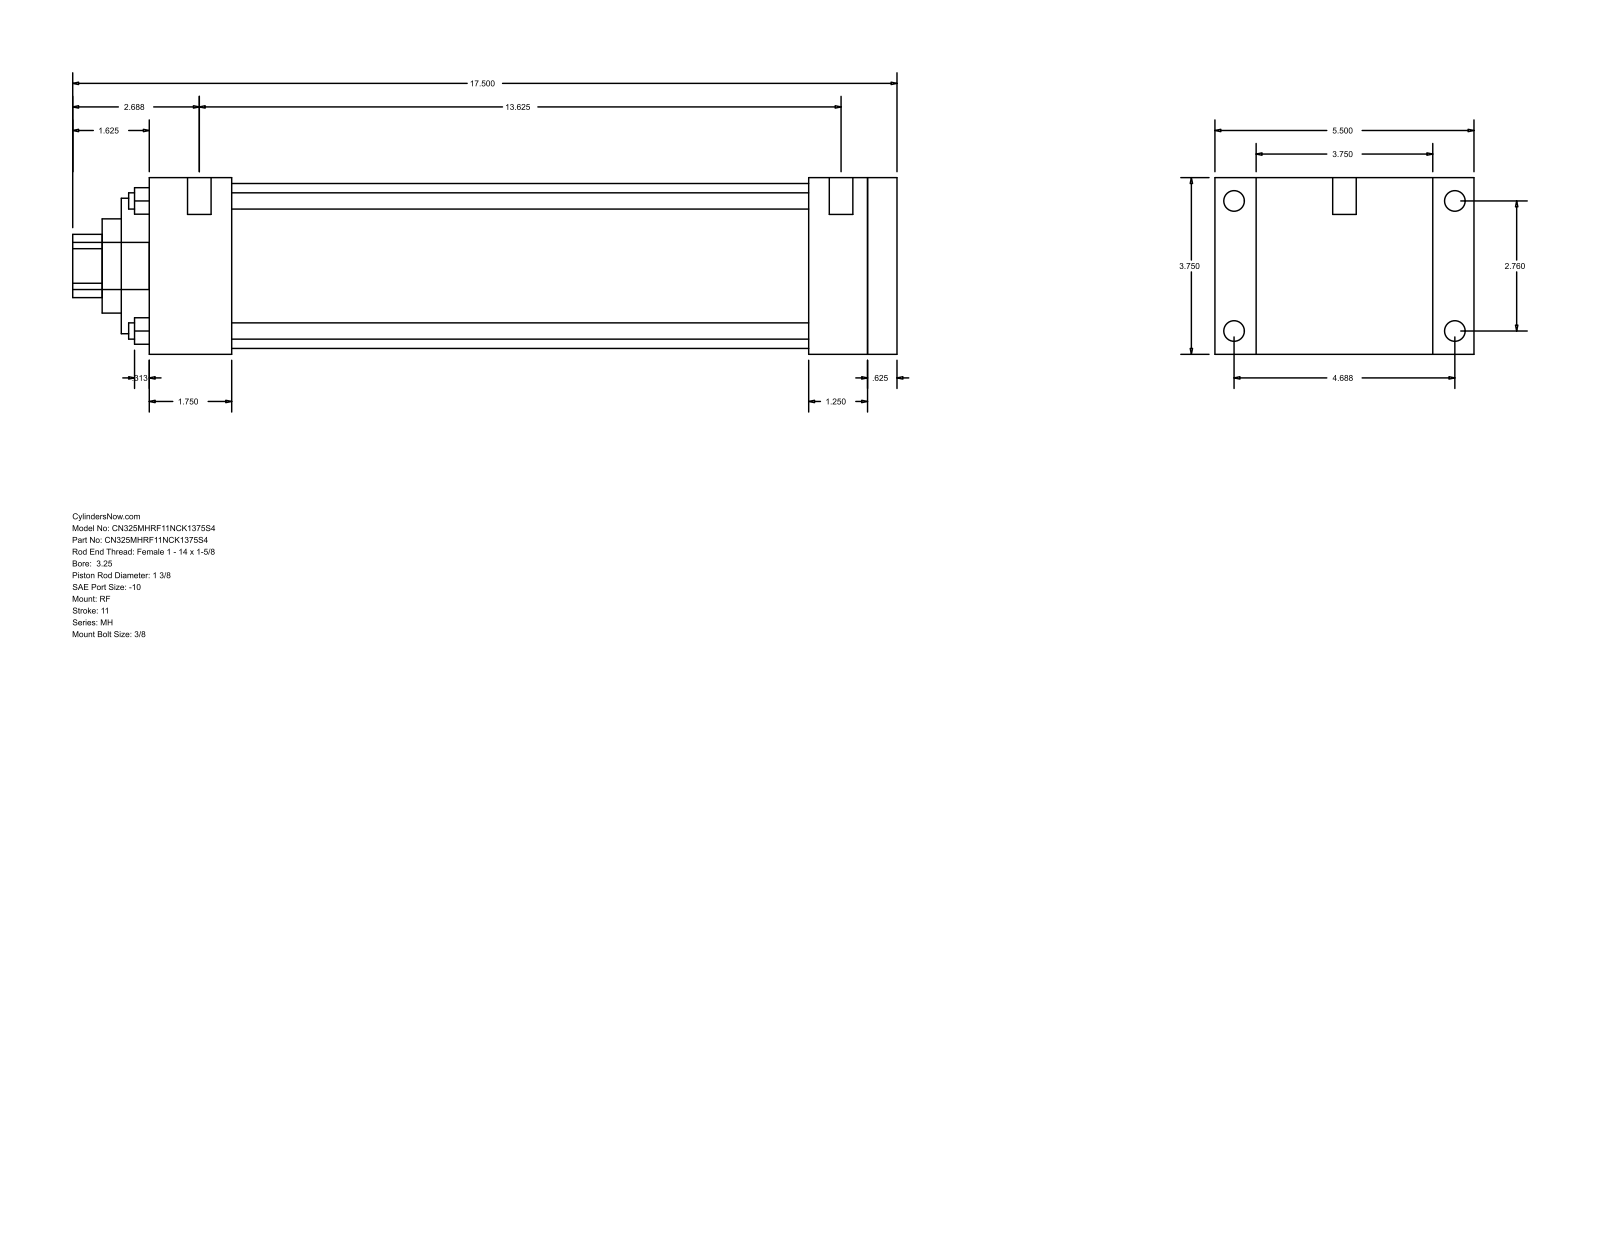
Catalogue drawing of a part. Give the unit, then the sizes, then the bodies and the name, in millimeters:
Units: millimetres
Overall size (bounding box): 444.5 × 139.7 × 95.25
Round holes (diameter × count): ⌀8.76 ×4, ⌀34.92 ×1, ⌀50.8 ×1, ⌀73.03 ×1, ⌀88.9 ×1
Round bosses / shafts (diameter × count): ⌀11.13 ×4, ⌀5.56 ×4, ⌀12.7 ×2, ⌀25.4 ×1
Partial cylindrical surfaces — rounded edges, fillets, slot ends (radius × count): R17.06 ×1
Main face-to-face distances: 95.24, 403.23, 15.88, 387.35, 22.23, 117.47, 44.45, 342.9, 358.78, 355.61
Hole centre spacings: 49.57, 70.1, 99.14
Bodies: 0 solids, 94 faces (65 planar, 29 cylindrical, 0 other)
Part name (STEP PRODUCT): MH_RF__0325_1.375
STEP written by: GSSL Pune (CONFIG_CONTROL_DESIGN)
